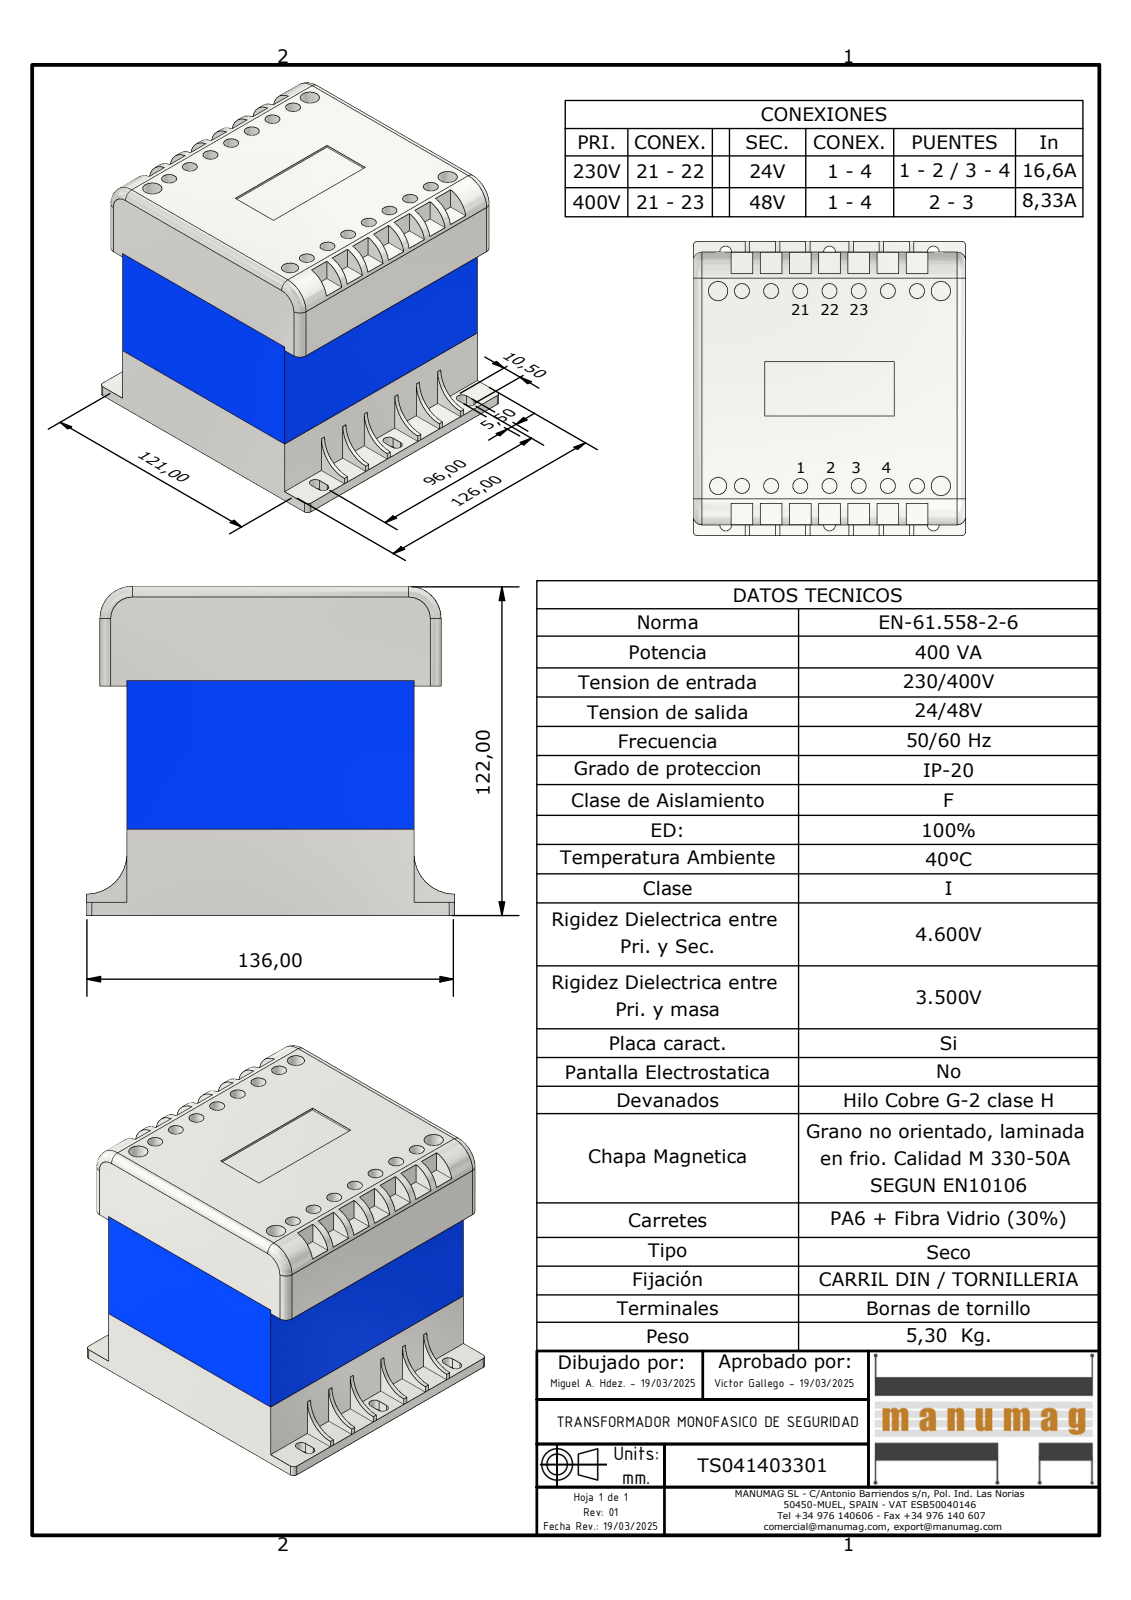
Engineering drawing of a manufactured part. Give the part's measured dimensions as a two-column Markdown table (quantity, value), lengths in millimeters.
| quantity | value |
| --- | --- |
| part name | TS041403301; INFERIOR EI120; CENTRAL EI120-50; SUPERIOR EI120 |
| STEP written by | Autodesk Inventor 2023 (AUTOMOTIVE_DESIGN) |
| units | millimeters |
| bodies | 15 solids, 244 faces (186 planar, 54 cylindrical, 4 other) |
| overall size | 136 × 126 × 122 |
| volume | 656 709 mm³ |
| surface area | 172 452 mm² |
| round holes (diameter × count) | 7 × 14, 9 × 3, 8 × 1 |
| partial cylindrical surfaces (radius × count) | 2.75 × 12, 4 × 6, 2 × 4, 12 × 2, 15 × 2 |
| main face-to-face distances | 1, 105, 5, 125, 126, 87, 82, 106, 104, 122 |
| hole center spacings | 13.5, 91.01, 27, 93.96, 90, 40.5, 98.69, 54 |
